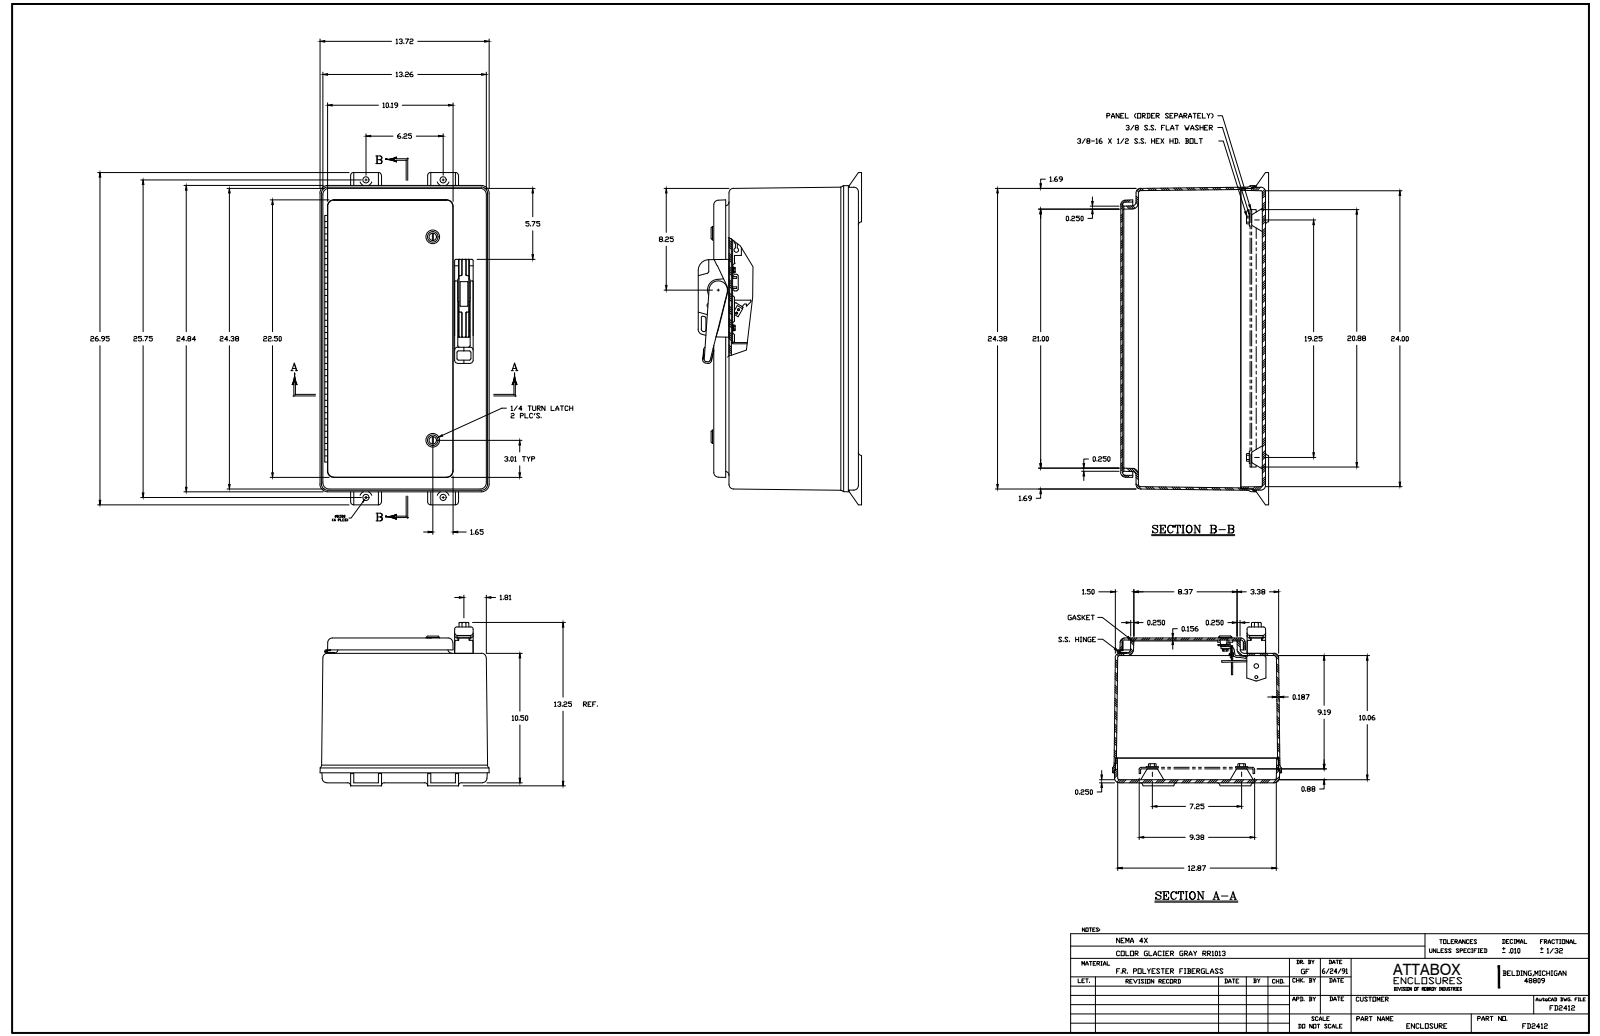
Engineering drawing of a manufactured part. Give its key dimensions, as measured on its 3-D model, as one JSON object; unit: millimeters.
{"part_name": "FD2412", "step_written_by": "SolidWorks 2018 (AUTOMOTIVE_DESIGN)", "units": "millimeters", "bodies": {"solids": 78, "faces": 2245, "planar": 1102, "cylindrical": 669, "other": 474}, "overall_size": [684.5, 348.5, 336.6], "volume_mm3": 6242000, "surface_area_mm2": 2692000, "round_holes": [[3.8, 10], [4.7, 8], [12.7, 8], [6.5, 6], [4.3, 4], [5.5, 4], [7.1, 4], [7.8, 4], [7.9, 4], [11, 4], [14.3, 4], [4.4, 3]], "round_bosses_or_shafts": [[7.6, 8], [25.4, 4], [9.5, 4], [9.1, 4], [5.1, 4], [4.8, 4], [7.9, 3], [6.4, 3]], "partial_cylinders_radius": [[6.4, 37], [3.2, 19], [4.8, 14], [12.7, 12], [4.7, 11], [9.5, 10], [8, 9], [2.4, 8]], "face_to_face_distances": [4.7, 6.4, 294.1, 287.8, 4, 298.1, 291.7, 25.5, 31.9, 262.3], "hole_center_spacings": [7.1, 157.1, 83.5, 163.9, 190.3, 314.2, 419.1, 571.7]}
